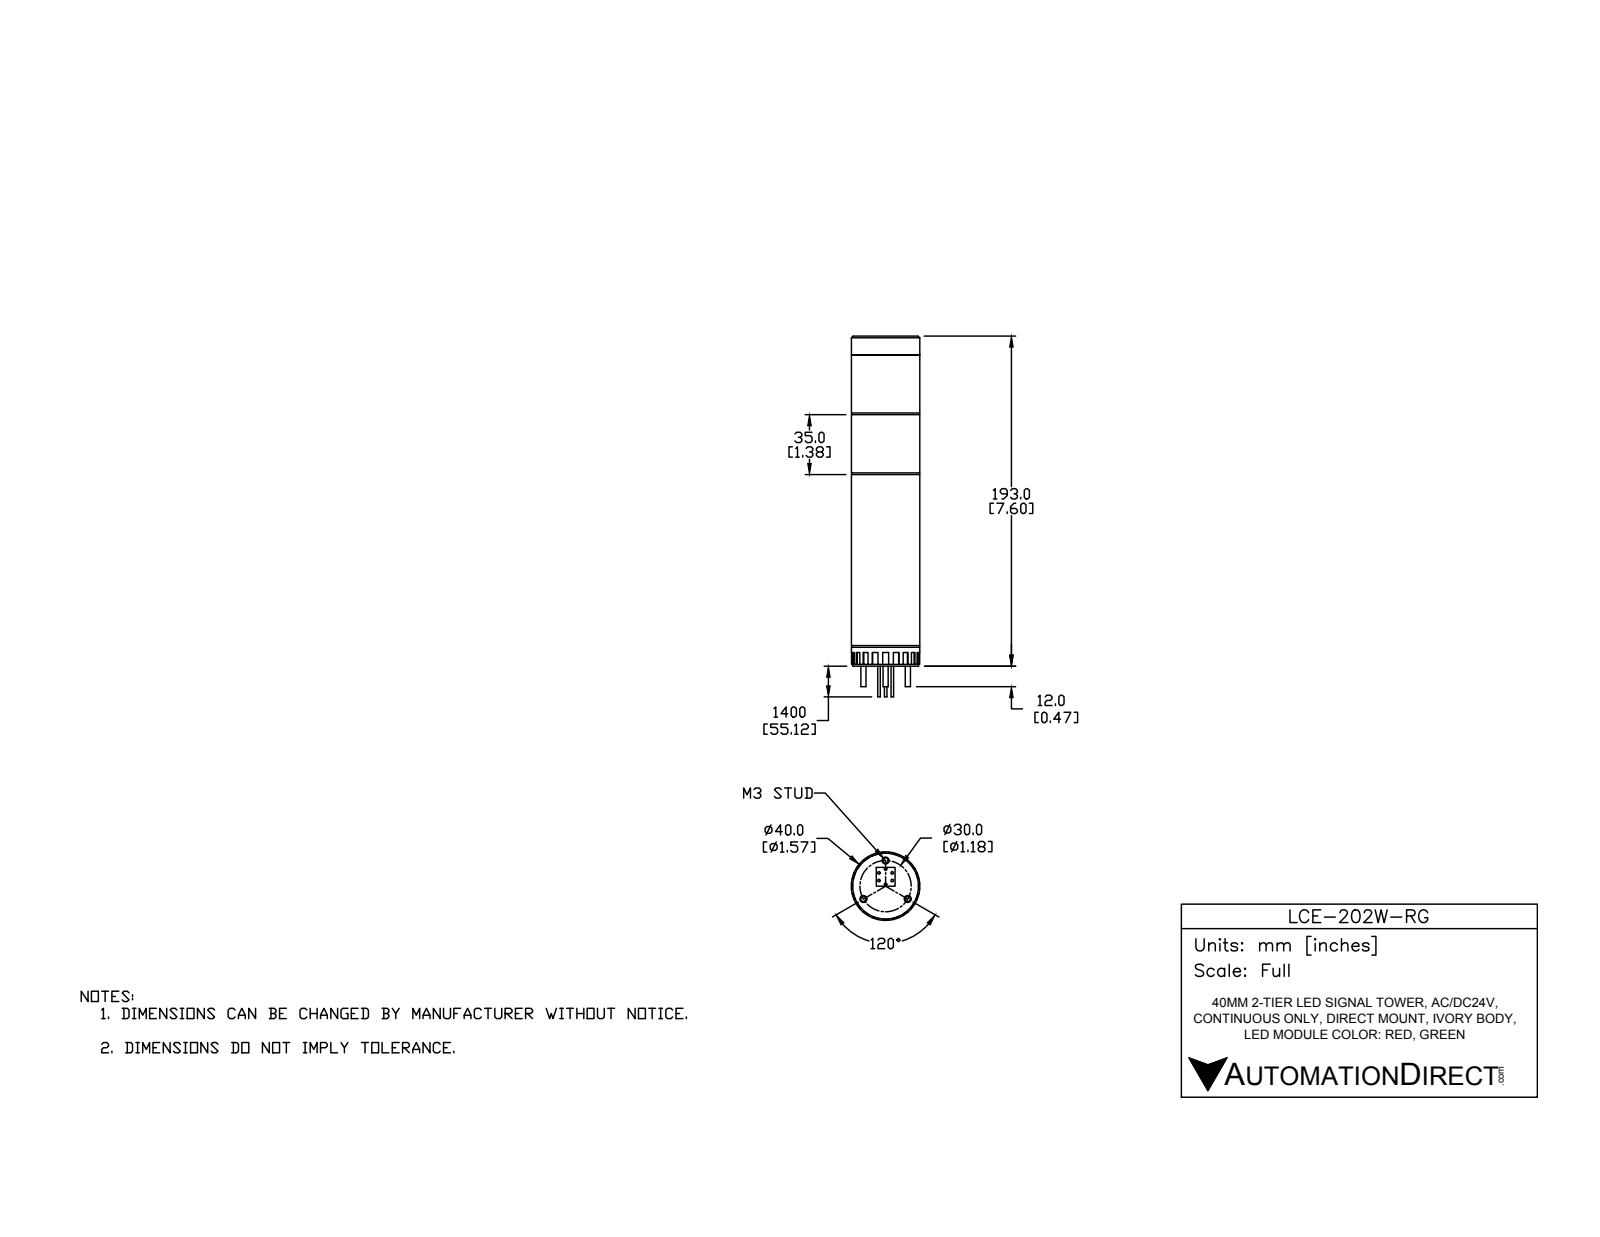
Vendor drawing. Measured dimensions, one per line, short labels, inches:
name: LCE-202W-RG
written by: SolidWorks 2016 (AUTOMOTIVE_DESIGN)
unit: in
bodies: 19 solids, 194 faces (144 planar, 46 cylindrical, 4 other)
size: 8.307 × 1.575 × 1.575
volume: 14.7 in³; area: 74.07 in²
holes: 3× ⌀0.157, 1× ⌀0.315
bosses: 6× ⌀0.059, 3× ⌀0.118, 1× ⌀1.575, 1× ⌀1.555, 1× ⌀1.516, 1× ⌀0.217
face distances: 0.039, 1.378, 1.339, 3.976, 5.354, 0.433, 7.126, 4.409, 5.787, 1.417
hole spacings: 0.591, 1.023
